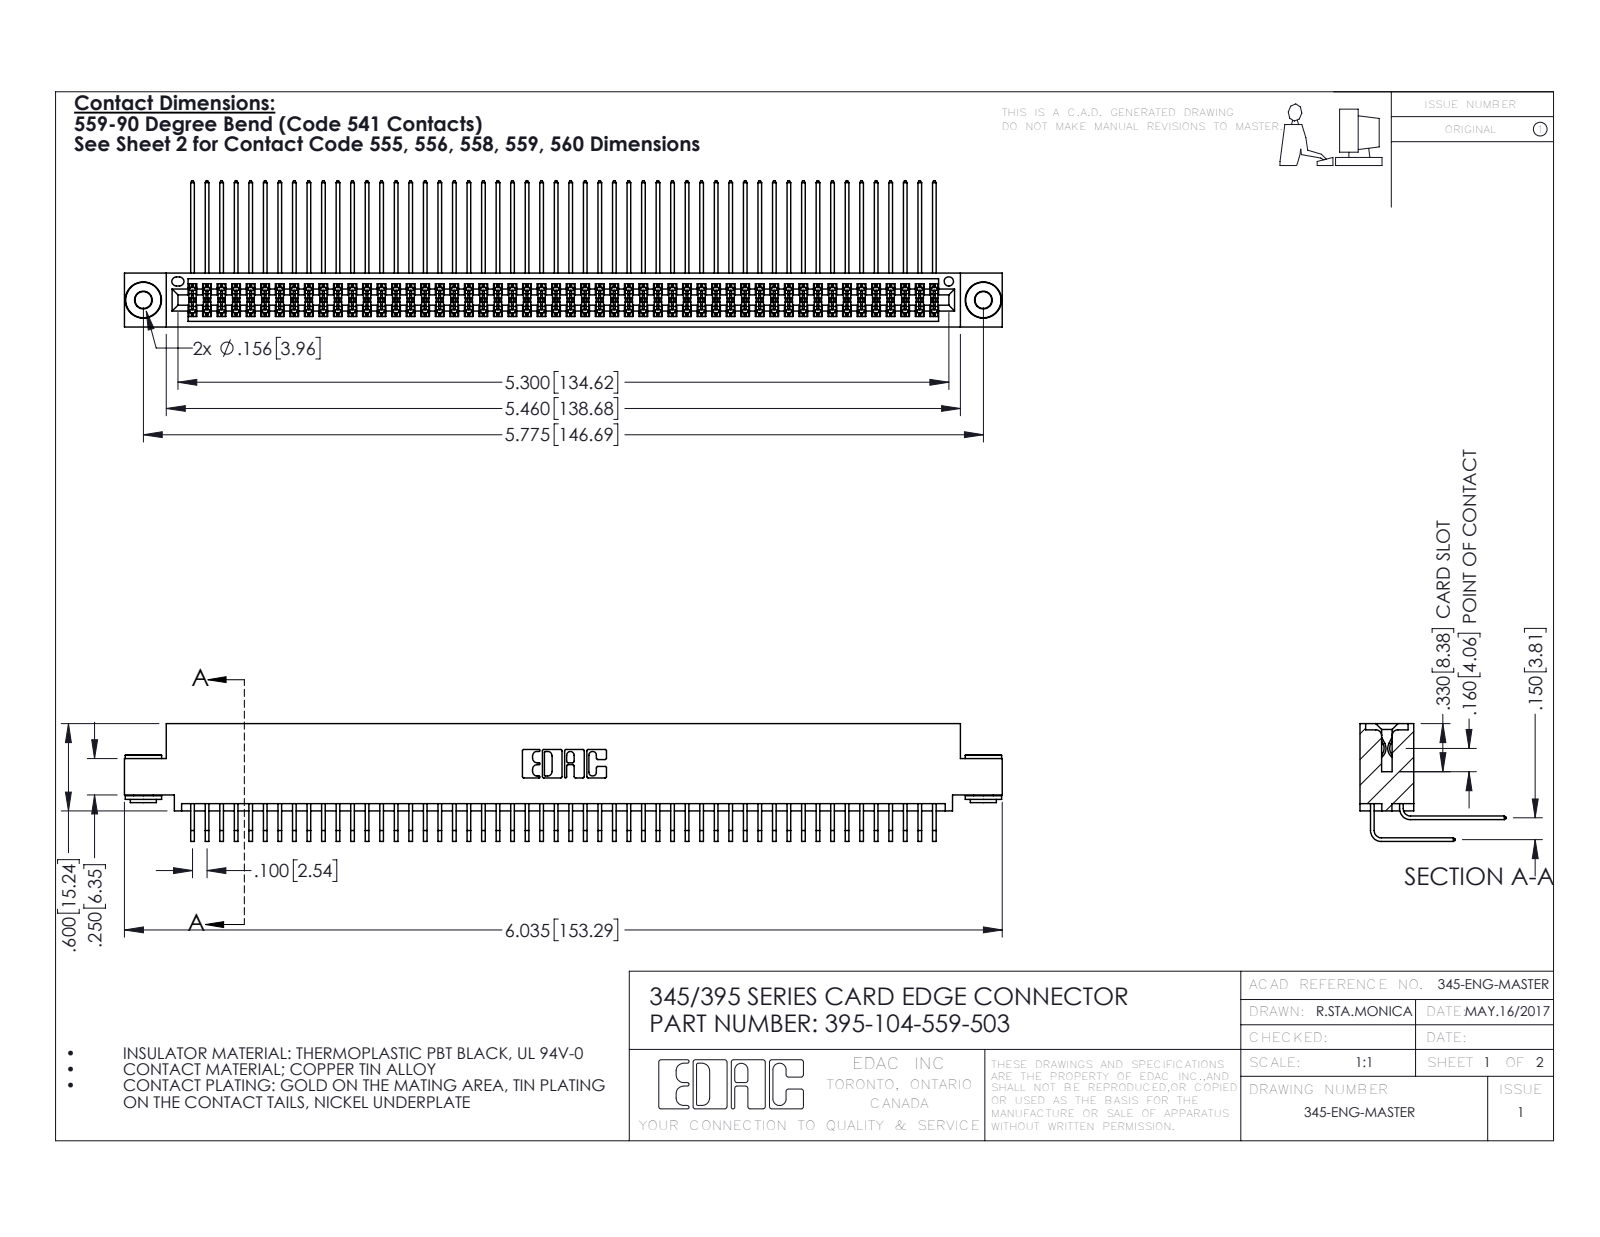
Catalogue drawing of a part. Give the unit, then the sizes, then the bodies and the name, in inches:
Units: inches
Overall size (bounding box): 6.035 × 1.005 × 0.809
Round holes (diameter × count): ⌀0.116 ×2, ⌀0.156 ×2, ⌀0.064 ×1
Round bosses / shafts (diameter × count): ⌀0.25 ×2, ⌀0.18 ×2, ⌀0.136 ×2
Partial cylindrical surfaces — rounded edges, fillets, slot ends (radius × count): R0.006 ×156, R0.01 ×22, R0.007 ×6, R0.031 ×6, R0.026 ×3, R0.014 ×2, R0.019 ×2, R0.022 ×2
Main face-to-face distances: 0.072, 0.298, 0.2, 0.37, 0.025, 0.098, 0.272, 0.225, 0.175, 0.15
Hole centre spacings: 0.27, 5.539, 5.775
Volume: 0.948 in³ · Surface area: 40.72 in²
Bodies: 107 solids, 5576 faces (3734 planar, 1834 cylindrical, 8 other)
Part name (STEP PRODUCT): 345-250-002_345-250-002-102; 395-104-559-503; 345-292-001_559 Tail - 2; 345 Part_0.110 Offset - 0.156 Dia-TH (+1 more)
STEP written by: SolidWorks 2016 (CONFIG_CONTROL_DESIGN)
